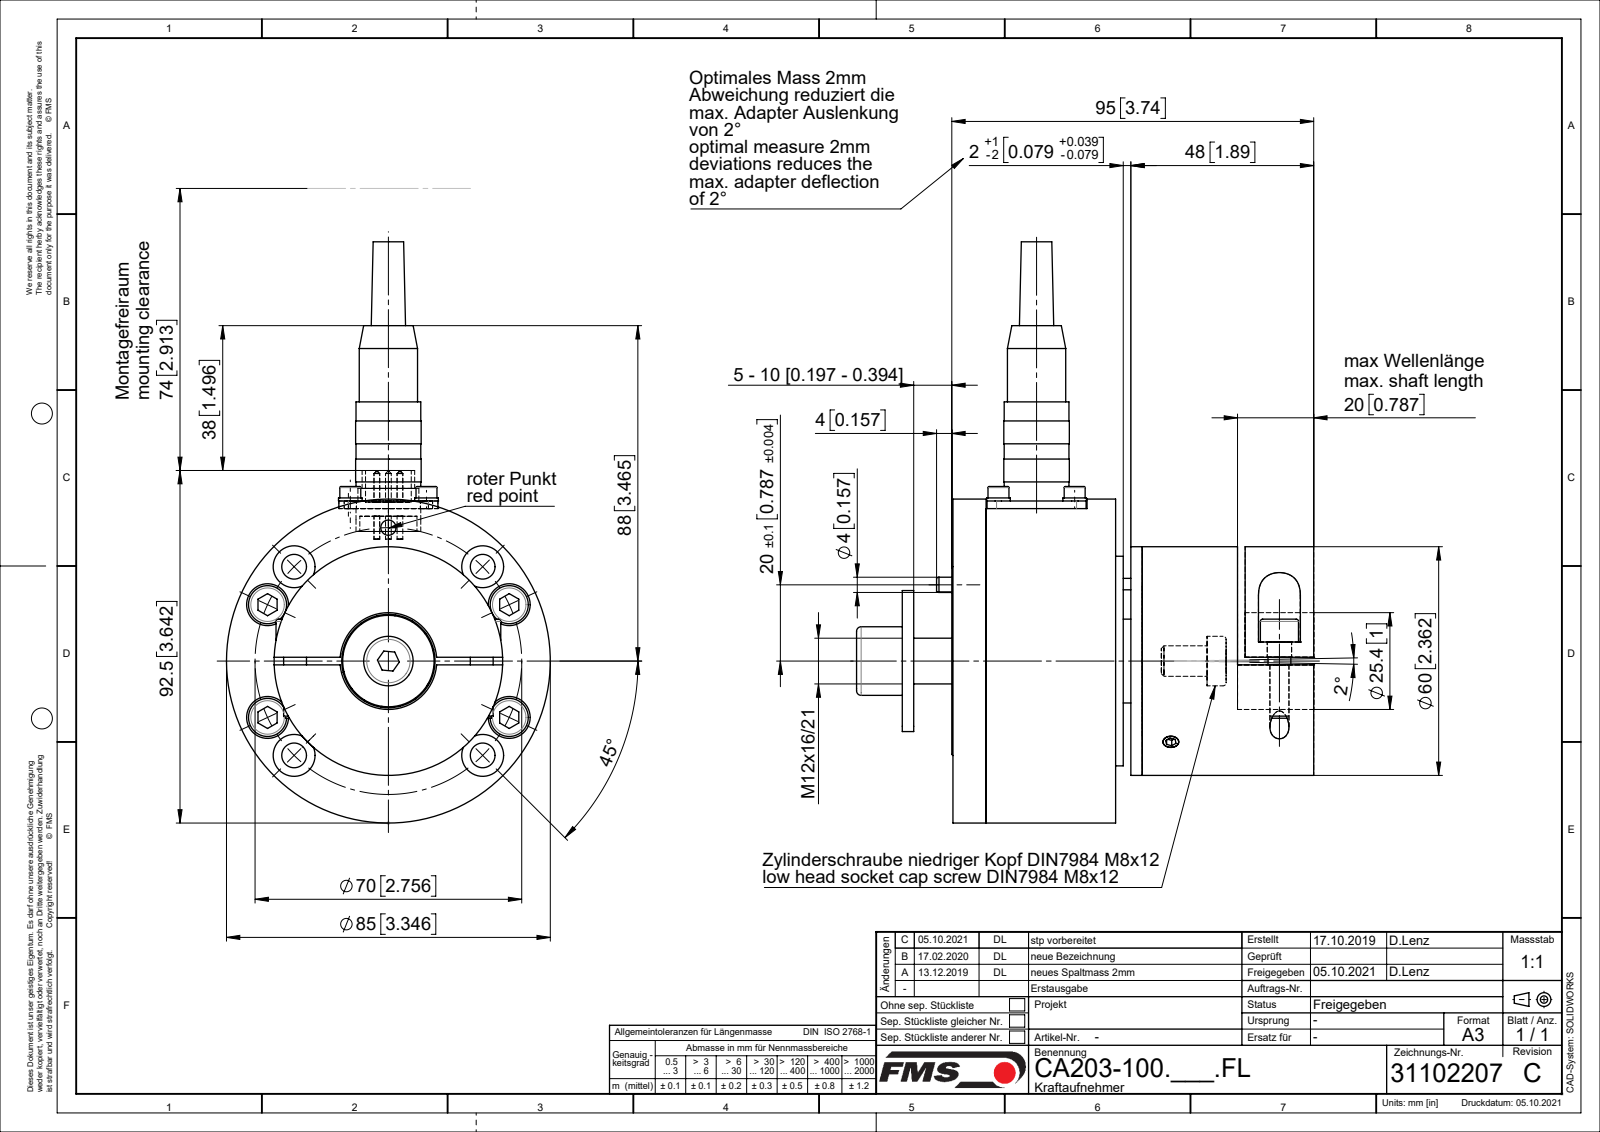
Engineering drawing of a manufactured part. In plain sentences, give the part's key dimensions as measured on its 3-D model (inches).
The part is named "31102207_C; 070907-2_01; Sch DIN9021_M8; 31102201_01 (+8 more)". Its 3-D file was written by "SolidWorks 2018 (CONFIG_CONTROL_DESIGN)". It is 43 solids with 785 faces: 270 planar, 326 cylindrical and 189 other. Overall it measures 6.004 by 4.724 by 3.346 inches. Its volume is 19.05 cubic inches and its surface area 173.2 square inches. Round holes: 8 of diameter 0.098, 8 of diameter 0.256, 8 of diameter 0.433, 6 of diameter 0.197, 5 of diameter 0.157, 4 of diameter 0.122, 4 of diameter 0.126, 4 of diameter 0.142, 4 of diameter 0.276, 2 of diameter 0.118, 2 of diameter 0.252, 1 of diameter 0.165. Round bosses or shafts: 8 of diameter 0.118, 7 of diameter 0.236, 6 of diameter 0.394, 5 of diameter 0.059, 4 of diameter 0.244, 4 of diameter 0.224, 4 of diameter 0.217, 1 of diameter 3.346. Partial cylindrical surfaces (rounded edges, fillets, slot ends): 4 of radius 0.098, 2 of radius 0.197, 2 of radius 0.217. The main face-to-face distances are 0.079, 1.614, 1.772, 0.394, 1.181, 0.118, 1.969, 0.866, 2.362, 1.339. The hole center spacings are 1.378, 0.787, 0.976, 0.992, 1.291, 2.013, 2.223, 1.113.
